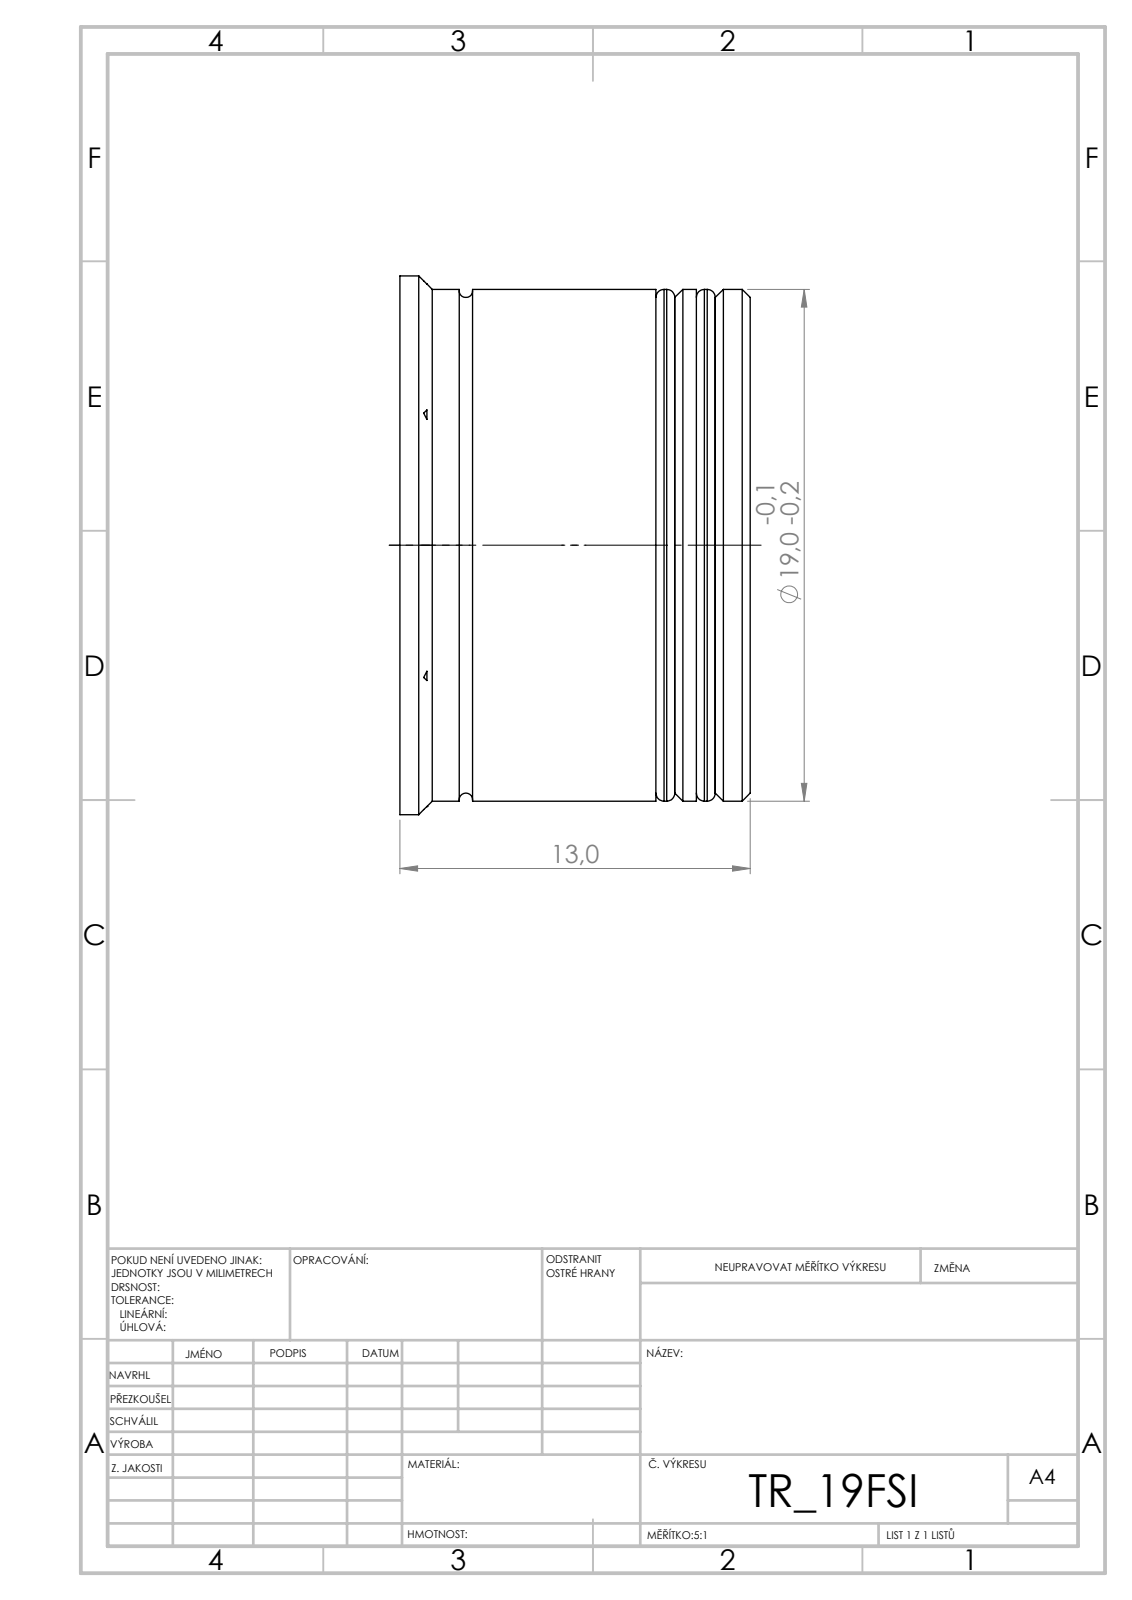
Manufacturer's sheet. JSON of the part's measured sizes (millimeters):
{"step_written_by": "SolidWorks 2019 (CONFIG_CONTROL_DESIGN)", "units": "millimeters", "bodies": {"solids": 3, "faces": 74, "planar": 29, "cylindrical": 25, "other": 20}, "overall_size": [20, 20, 13], "volume_mm3": 3828, "surface_area_mm2": 2760, "round_bosses_or_shafts": [[20, 1], [19, 1], [18.4, 1]], "partial_cylinders_radius": [[8, 1]], "face_to_face_distances": [1.5, 0.7, 2.2, 2, 3.5, 1.3, 2.8, 0.8, 12, 10.7]}
